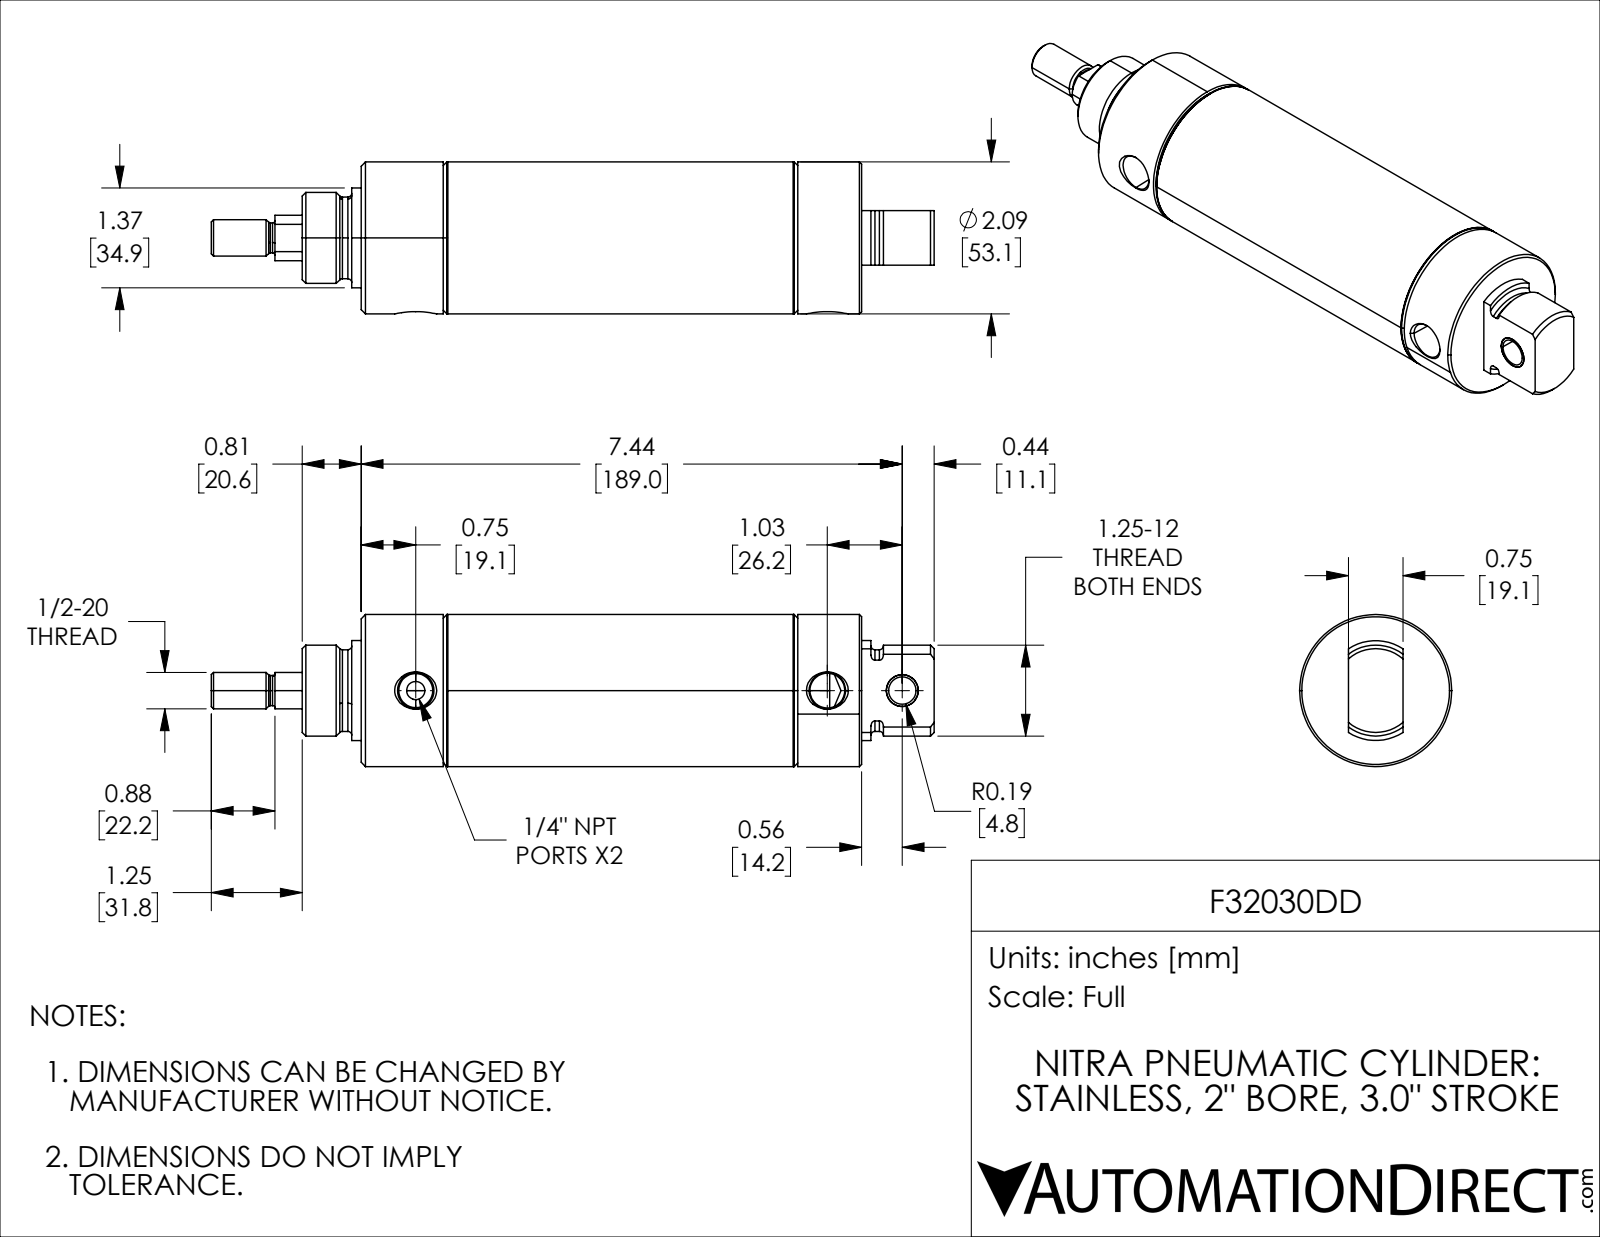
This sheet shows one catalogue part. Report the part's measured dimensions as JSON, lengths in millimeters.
{"part_name": "F32030DD_3; F32030DD_5; F32030DD_11; F32030DD (+2 more)", "step_written_by": "SolidWorks 2021 (CONFIG_CONTROL_DESIGN)", "units": "millimeters", "bodies": {"solids": 5, "faces": 160, "planar": 31, "cylindrical": 60, "other": 69}, "overall_size": [252.43, 53.09, 53.09], "volume_mm3": 262887, "surface_area_mm2": 90807, "round_holes": [[6.35, 1], [9.55, 1], [11.15, 1], [12.18, 1], [16.52, 1], [19.05, 1], [49.05, 1]], "round_bosses_or_shafts": [[53.09, 1], [51.16, 1], [34.87, 1], [31.75, 1], [28.51, 1], [15.88, 1], [12.7, 1], [11.15, 1]], "partial_cylinders_radius": [[14.25, 1]], "face_to_face_distances": [30.17, 76.2, 106.37, 136.6, 60.4, 30.23, 106.38, 30.18, 30.22, 38.15], "hole_center_spacings": [26.16, 26.17, 143.76, 169.92, 169.93]}
